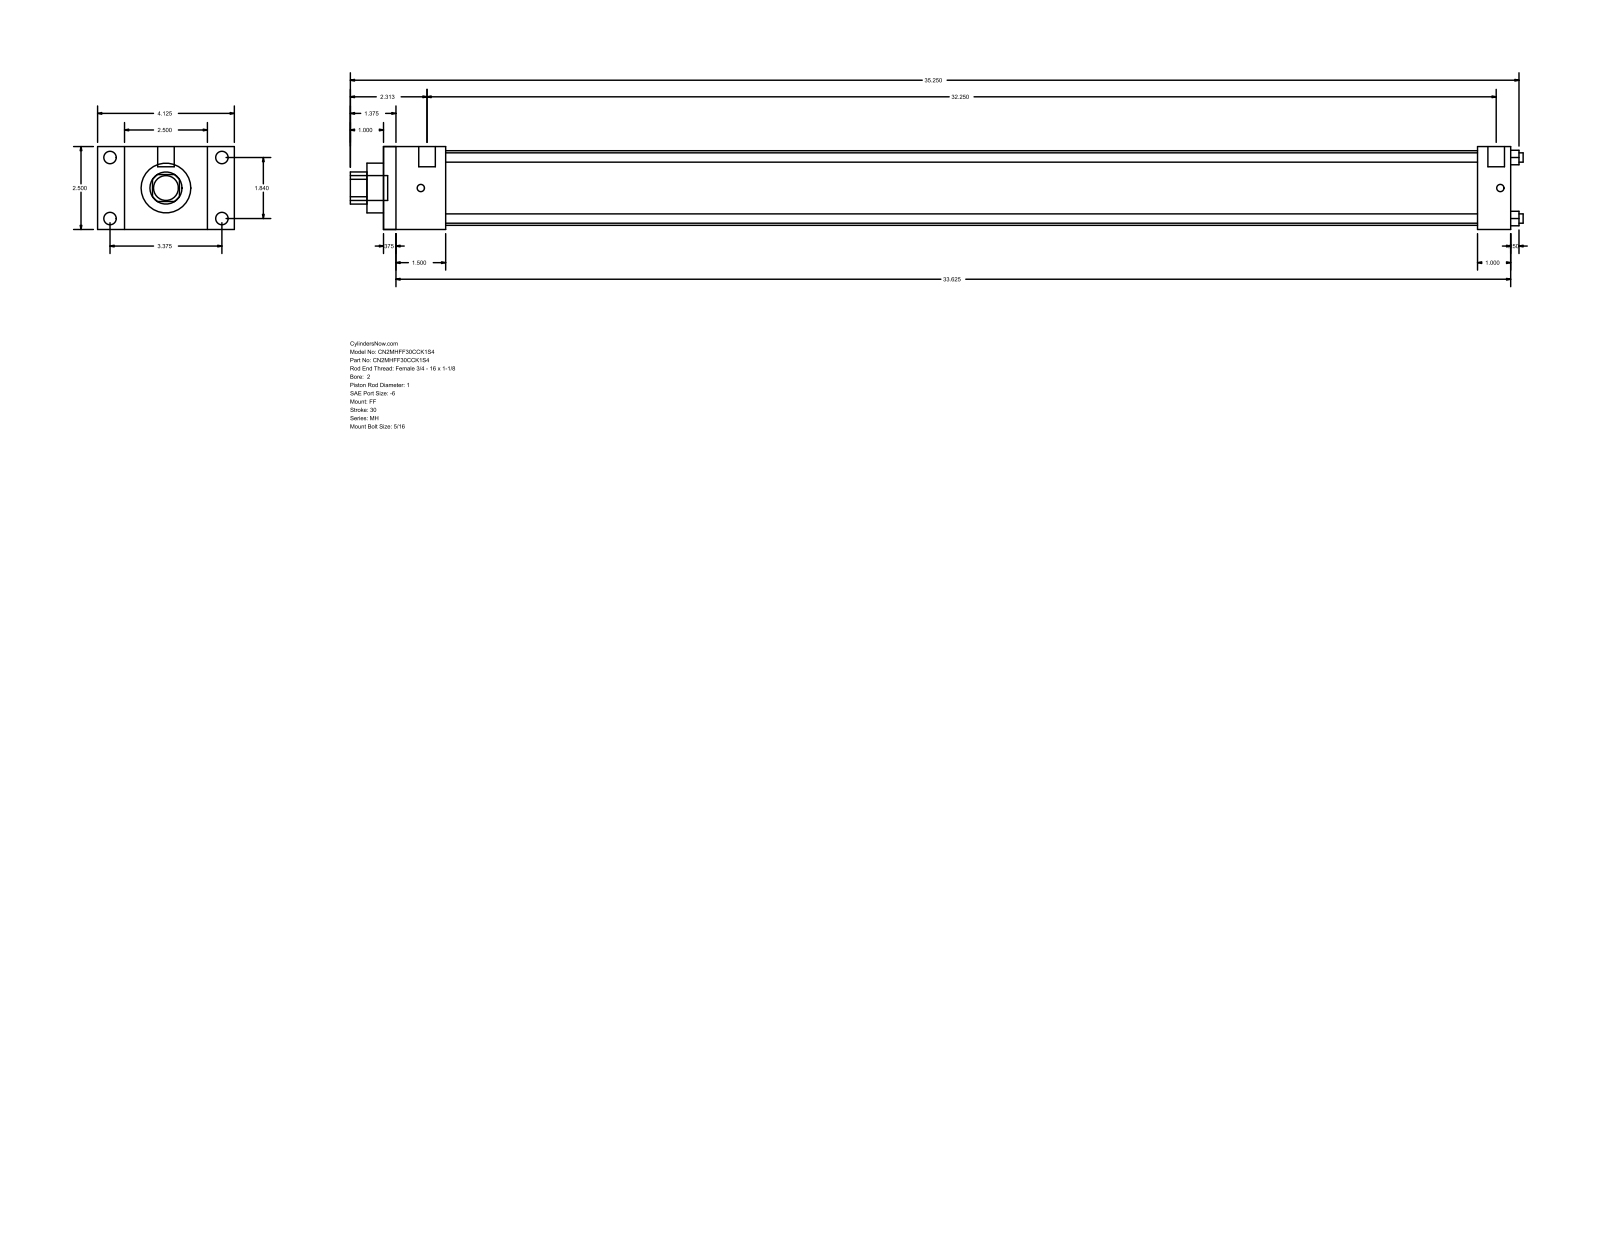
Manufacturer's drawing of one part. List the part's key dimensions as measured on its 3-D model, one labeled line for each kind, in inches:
Part name (STEP PRODUCT): MH_FF__0200_1
STEP written by: GSSL Pune (CONFIG_CONTROL_DESIGN)
Units: inches
Bodies: 0 solids, 92 faces (64 planar, 28 cylindrical, 0 other)
Overall size (bounding box): 35.375 × 4.125 × 2.5
Round holes (diameter × count): ⌀0.281 ×4, ⌀1 ×1, ⌀1.5 ×1, ⌀2.25 ×1
Round bosses / shafts (diameter × count): ⌀0.375 ×4, ⌀0.219 ×4, ⌀0.5 ×2, ⌀0.75 ×1
Partial cylindrical surfaces — rounded edges, fillets, slot ends (radius × count): R0.484 ×1
Main face-to-face distances: 2.5, 34, 0.375, 33.625, 0.813, 1, 1.875, 33, 1.5, 32.625
Hole centre spacings: 1.301, 1.84, 2.602
